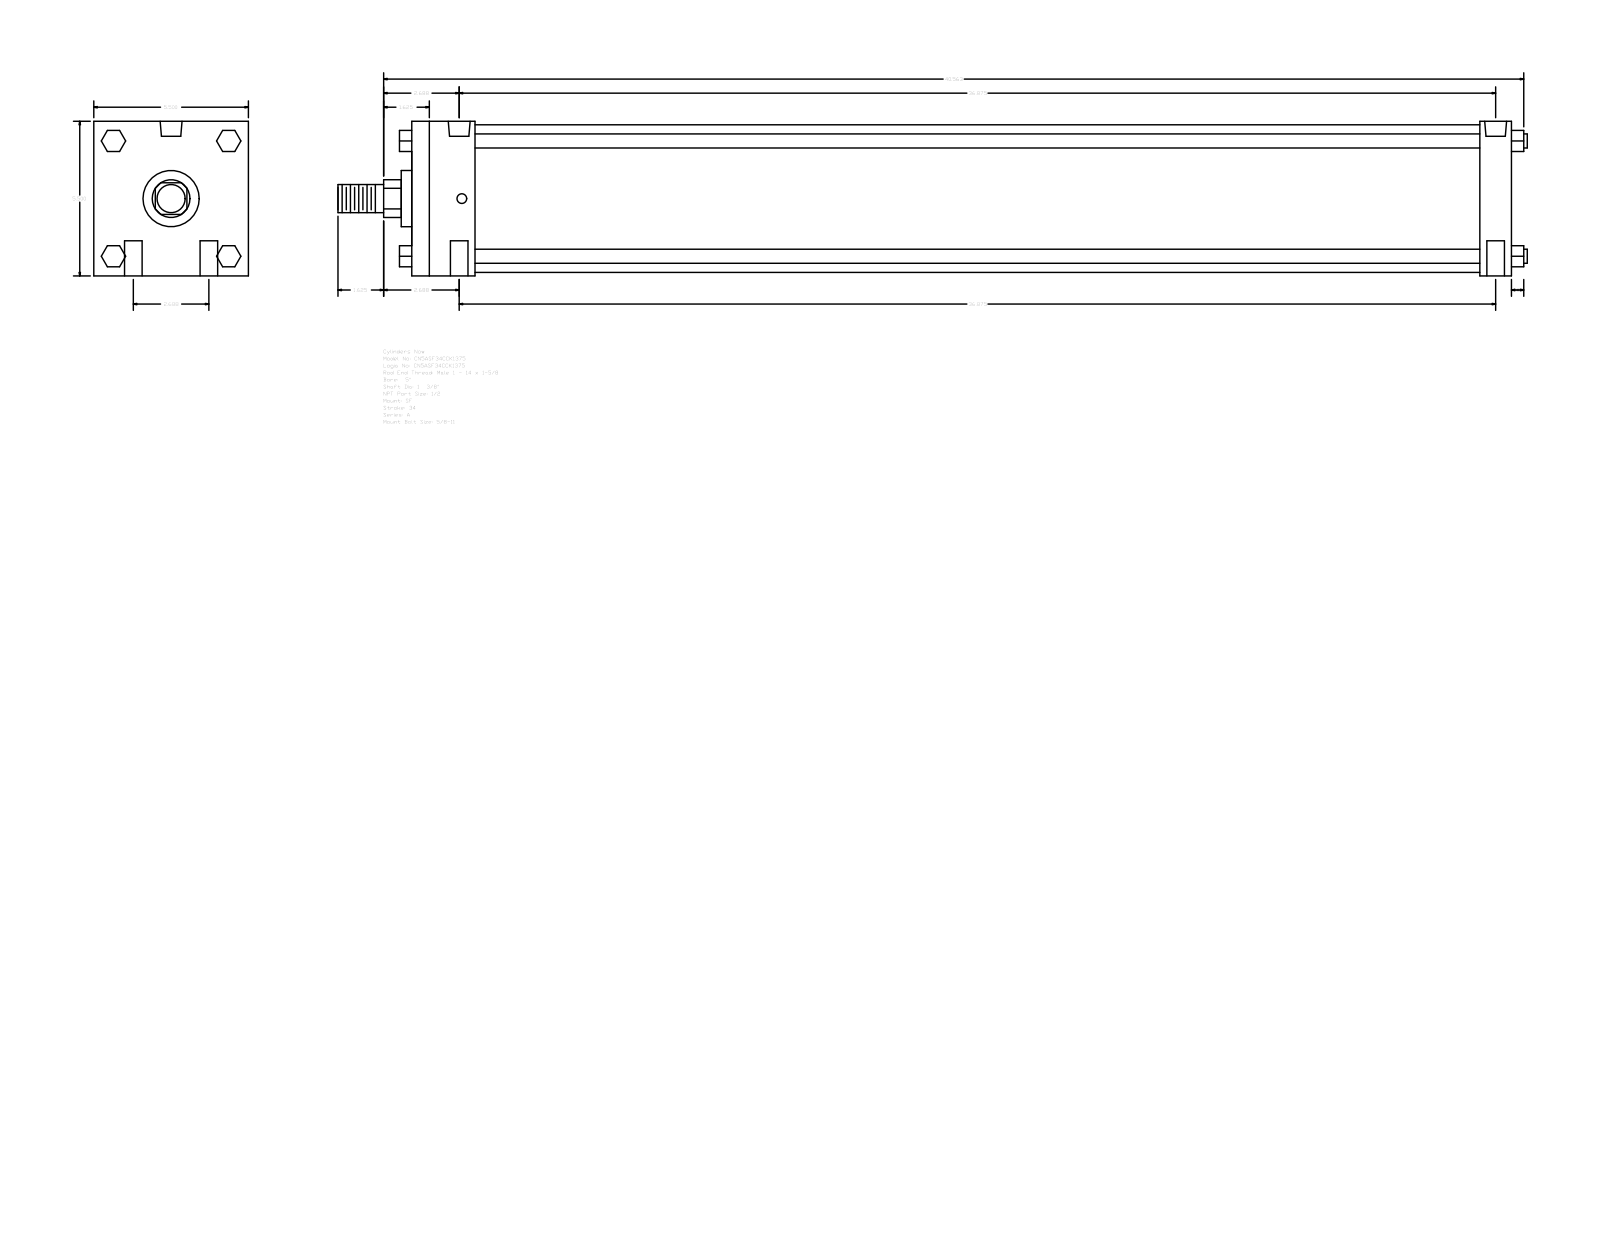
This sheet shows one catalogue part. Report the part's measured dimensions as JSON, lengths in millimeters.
{"part_name": "A_SF__0500_1.375", "step_written_by": "GSSL Pune (CONFIG_CONTROL_DESIGN)", "units": "millimeters", "bodies": {"solids": 0, "faces": 124, "planar": 94, "cylindrical": 30, "other": 0}, "overall_size": [1074.74, 139.7, 139.7], "round_holes": [[15.88, 4], [8.73, 2], [19.77, 2]], "round_bosses_or_shafts": [[12.7, 4], [133.35, 1], [50.8, 1], [34.92, 1], [25.4, 1]], "partial_cylinders_radius": [[17.06, 1]], "face_to_face_distances": [139.7, 993.77, 57.15, 965.2, 908.05, 936.62, 28.57, 19.05, 52.07, 90.18], "hole_center_spacings": [34.13, 937.25, 936.63, 68.26, 939.11, 931.85]}
